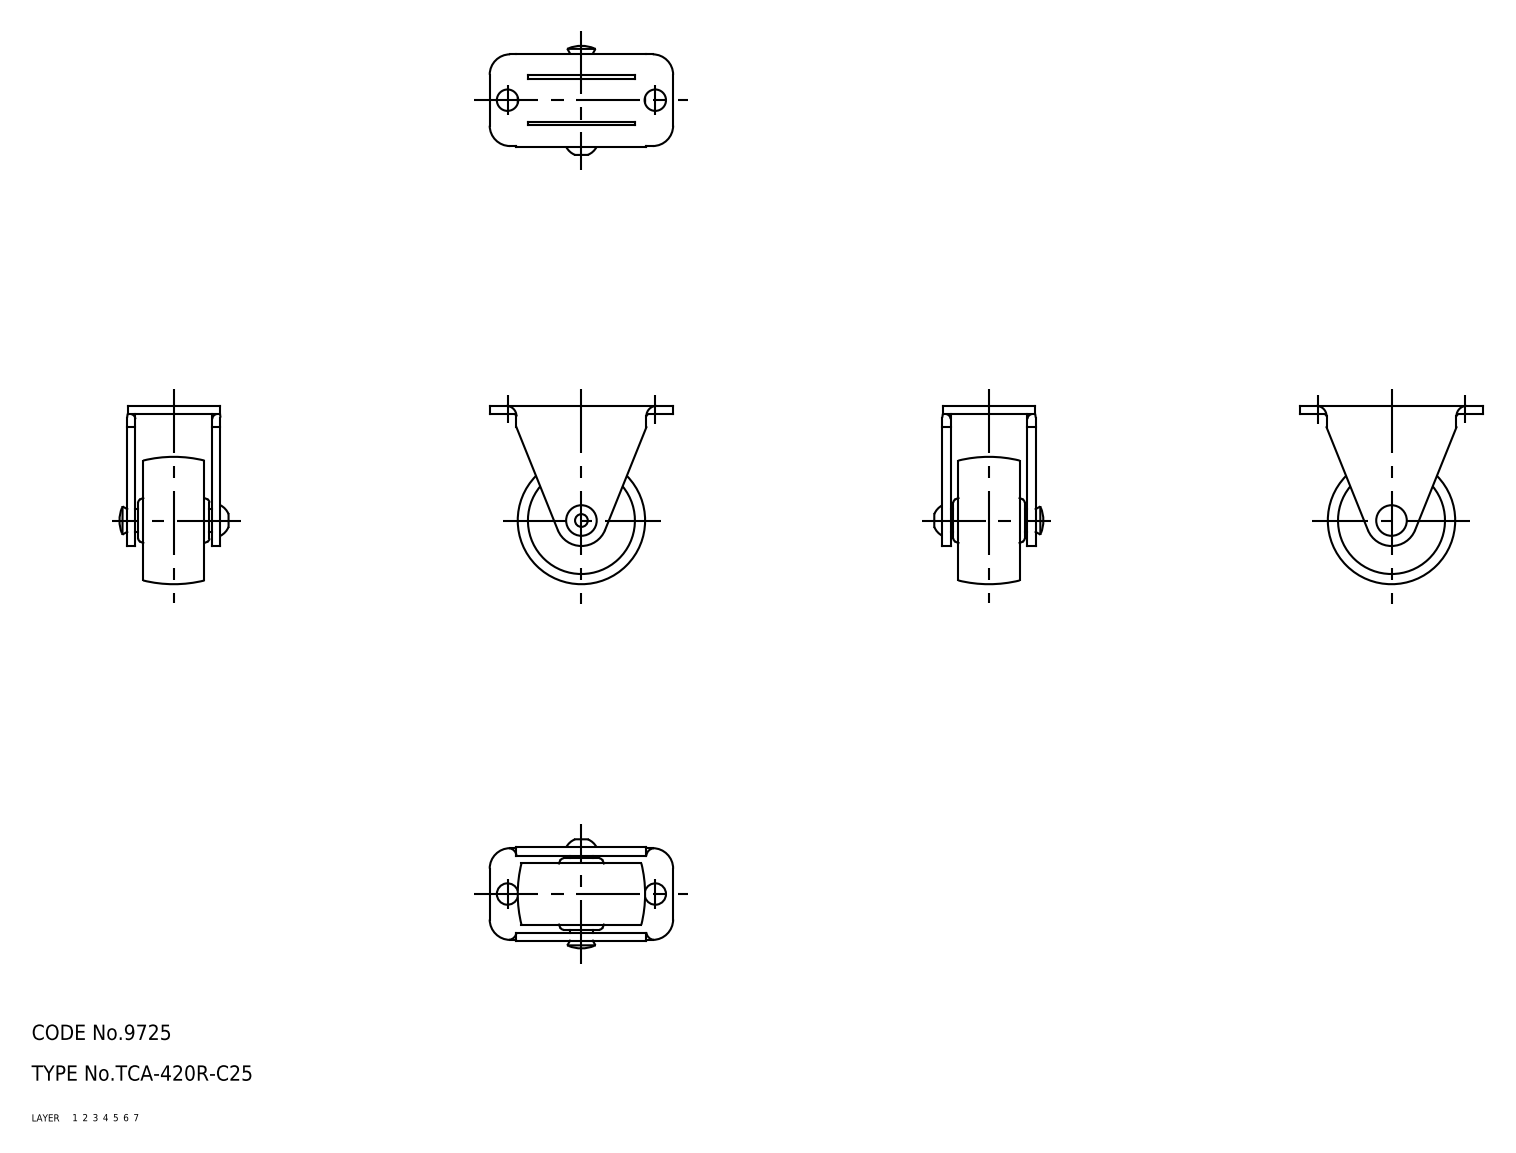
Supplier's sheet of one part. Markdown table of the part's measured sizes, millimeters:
| quantity | value |
| --- | --- |
| part name | wheel; axle; No_420_R_C25_1_32698_36 |
| STEP written by | CADfix (AUTOMOTIVE_DESIGN) |
| units | millimeters |
| bodies | 3 solids, 114 faces (0 planar, 0 cylindrical, 114 other) |
| overall size | 36 × 35 × 21.41 |
| volume | 6 844 mm³ |
| surface area | 5 970 mm² |
